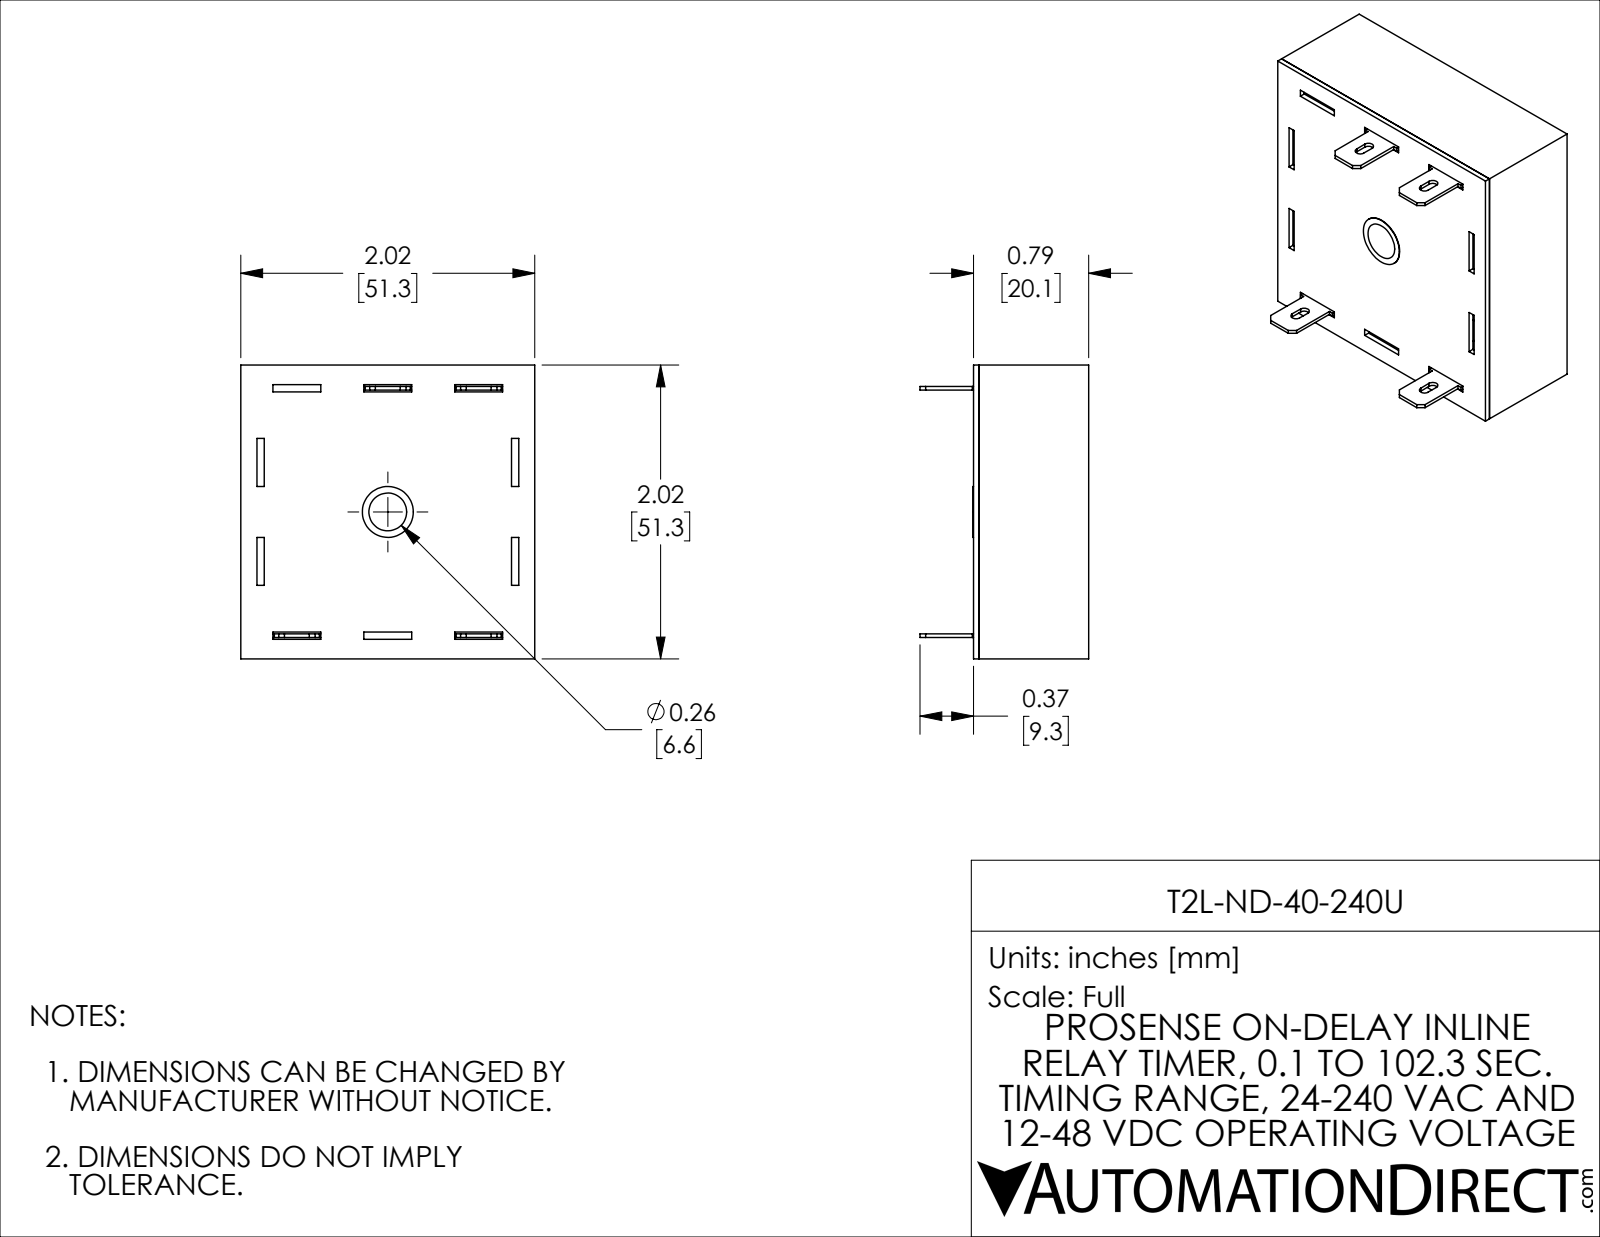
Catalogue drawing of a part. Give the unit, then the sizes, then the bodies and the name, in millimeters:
Units: millimetres
Overall size (bounding box): 51.31 × 51.31 × 29.46
Round holes (diameter × count): ⌀8.89 ×1
Partial cylindrical surfaces — rounded edges, fillets, slot ends (radius × count): R0.89 ×6
Main face-to-face distances: 1.14, 50.16, 19.15, 20.12, 0.97, 18.01, 18.98, 51.3, 49.02, 43.18
Volume: 10 499 mm³ · Surface area: 20 889 mm²
Bodies: 6 solids, 160 faces (146 planar, 12 cylindrical, 2 other)
Part name (STEP PRODUCT): T2L-ND-40-240U
STEP written by: SolidWorks 2021 (CONFIG_CONTROL_DESIGN)
